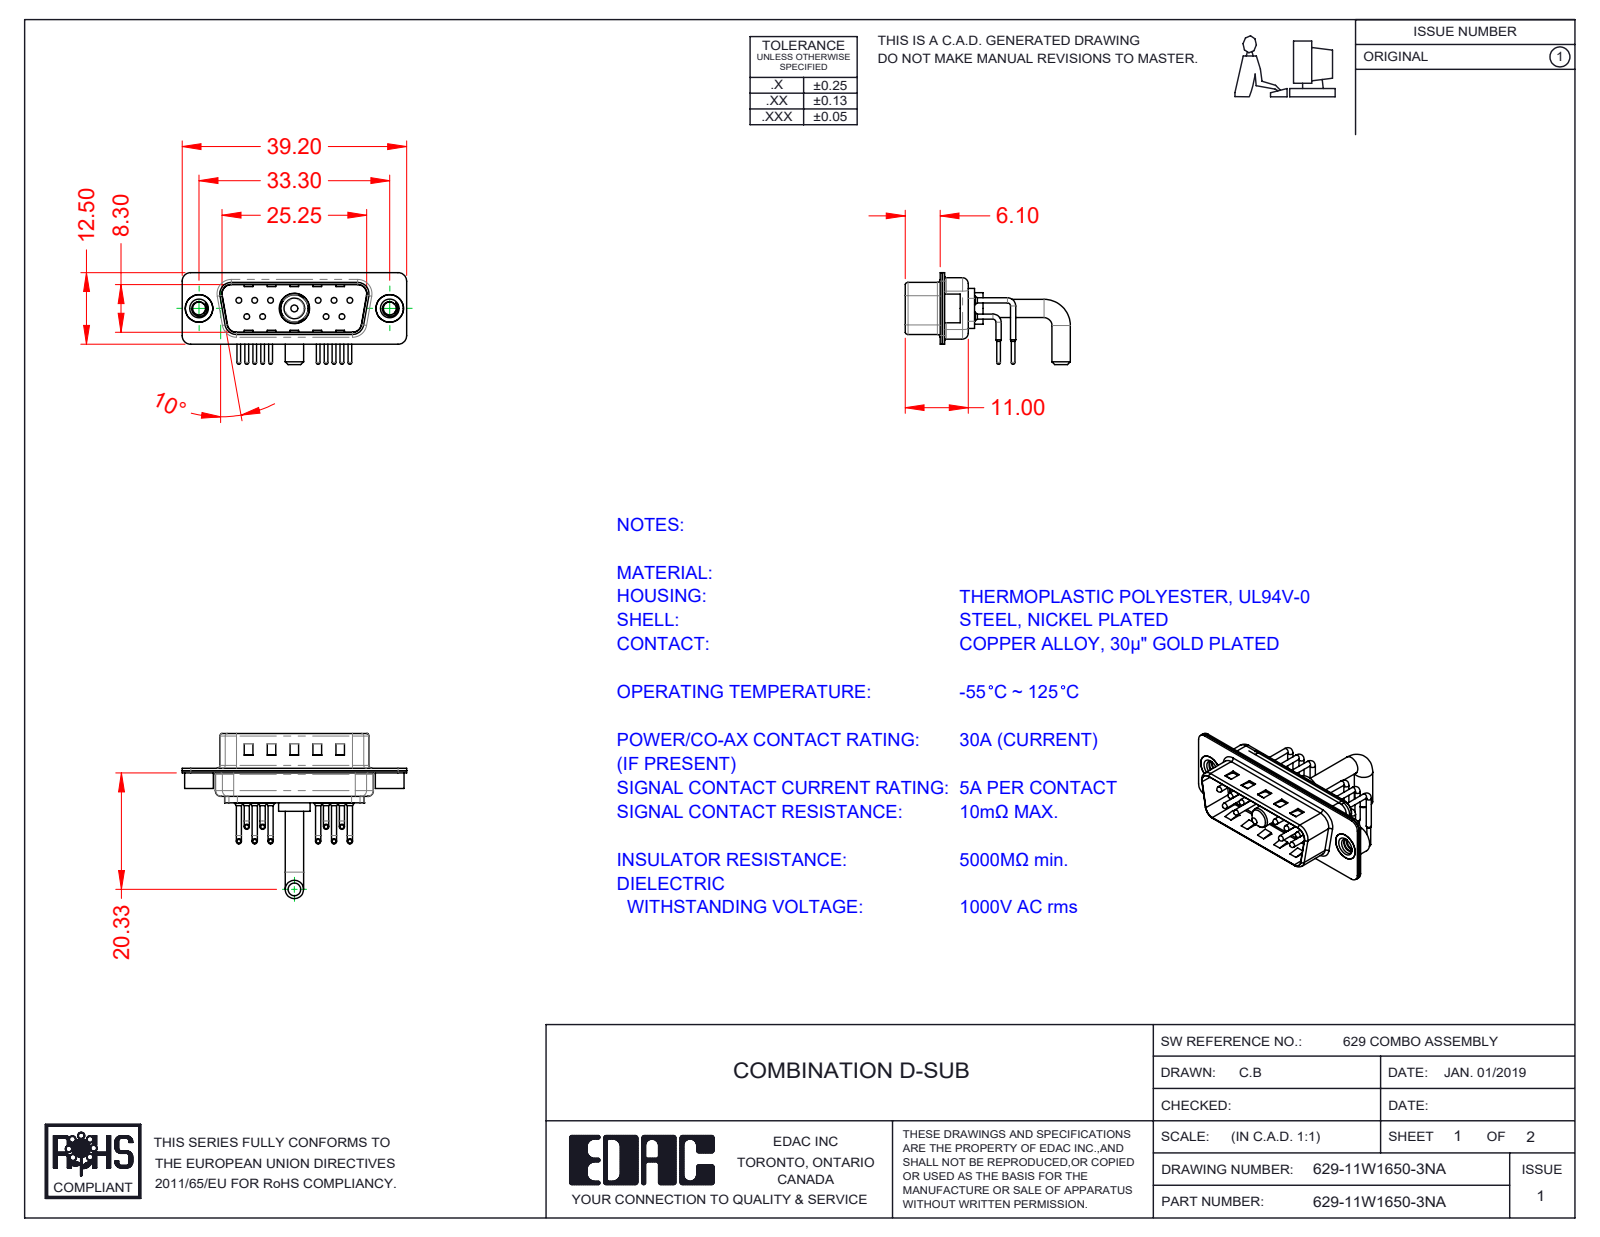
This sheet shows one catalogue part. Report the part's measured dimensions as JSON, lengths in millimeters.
{"part_name": "629Combo Shell Front_15 Contacts; 629Combo Contact Row 1; 629-11W1650-3NA; 629Combo Threaded Rivet_2 (+4 more)", "step_written_by": "SolidWorks 2020 (CONFIG_CONTROL_DESIGN)", "units": "millimeters", "bodies": {"solids": 17, "faces": 1496, "planar": 798, "cylindrical": 518, "other": 180}, "overall_size": [39.2, 28.83, 16.05], "volume_mm3": 2149, "surface_area_mm2": 5324, "round_holes": [[0.75, 10], [1.6, 10], [2, 10], [2.26, 2], [4, 2], [4.8, 2], [4.85, 1], [5.3, 1]], "round_bosses_or_shafts": [[0.9, 20], [1.5, 10], [1, 10], [0.65, 10], [5, 2], [4.9, 2], [3.2, 2], [5.5, 1]], "partial_cylinders_radius": [[1.5, 16], [2, 12], [1.01, 10], [0.5, 8], [1.6, 8], [1, 7], [0.25, 4], [0.6, 4]], "face_to_face_distances": [0.4, 0.8, 9.5, 9.1, 8.7, 9.9, 0.75, 5.6, 1.2, 0.35], "hole_center_spacings": [3.16, 2.77, 13.85, 11.08, 16.62, 5.03, 5.04, 5.54]}
